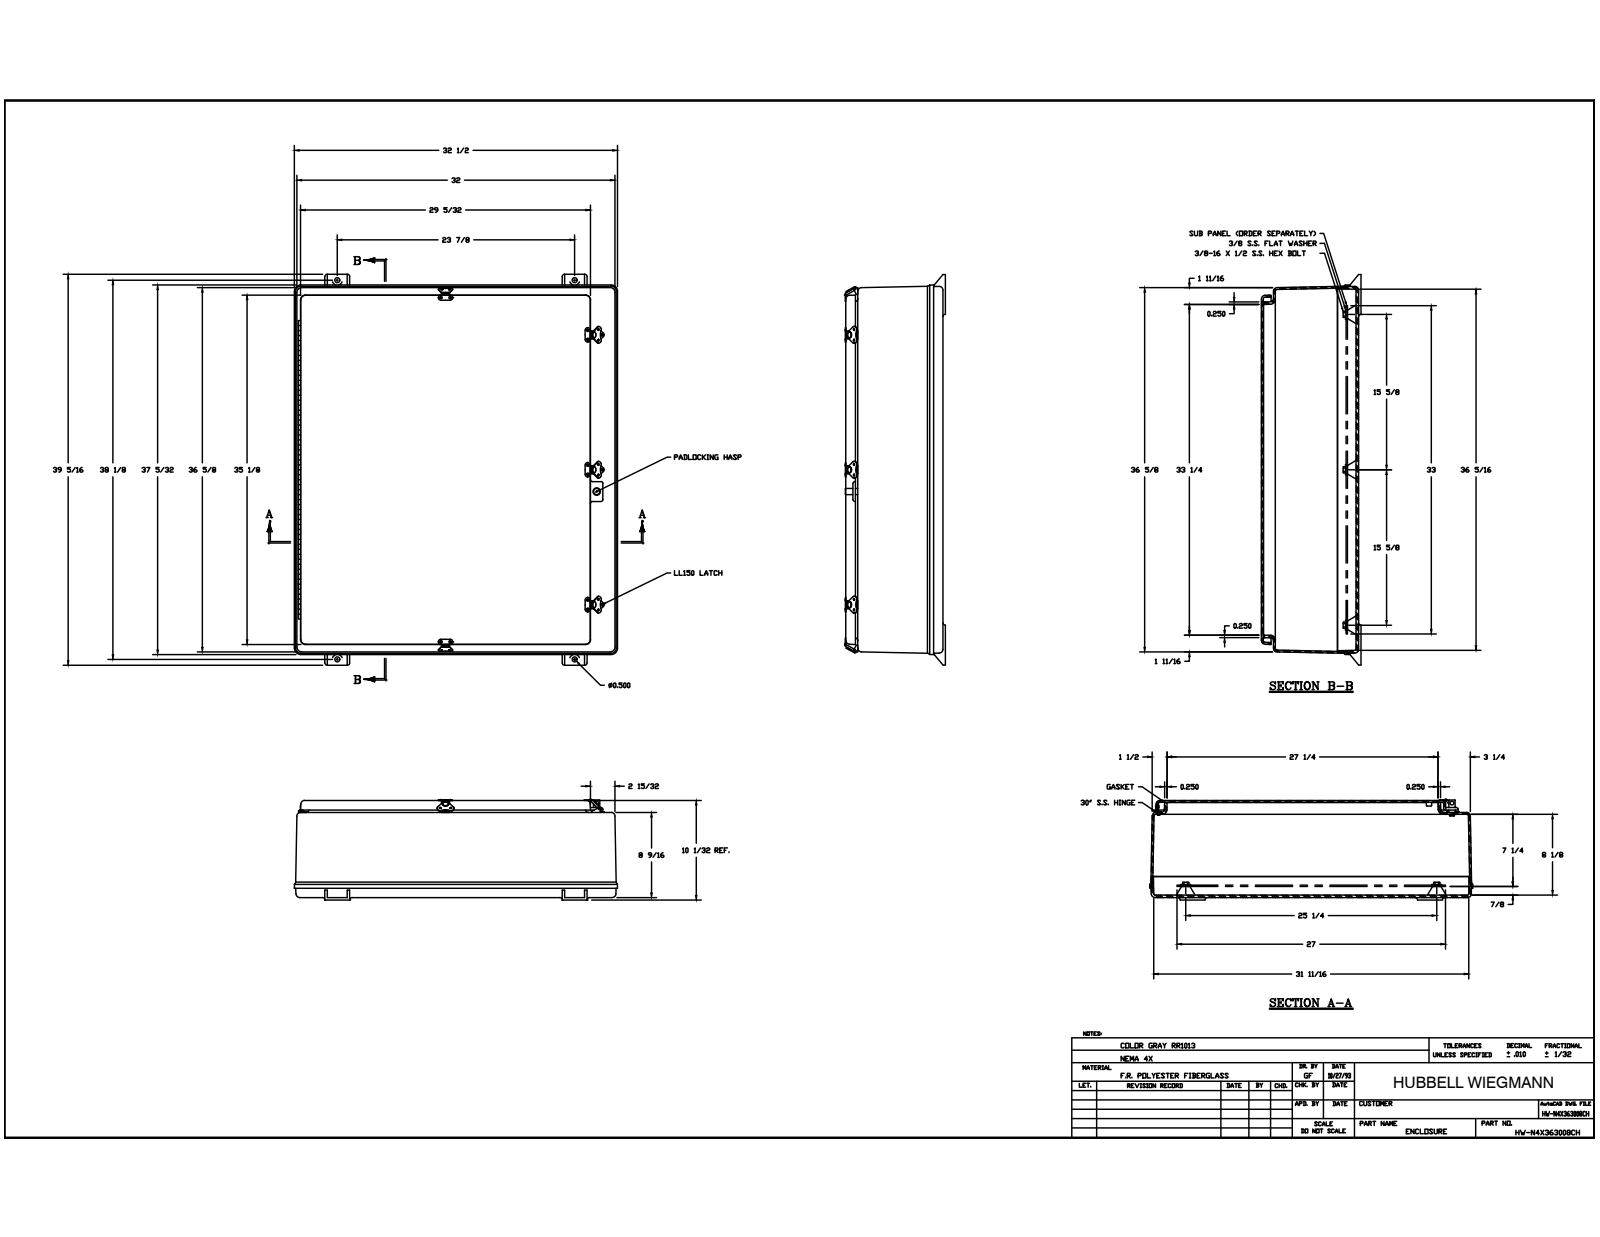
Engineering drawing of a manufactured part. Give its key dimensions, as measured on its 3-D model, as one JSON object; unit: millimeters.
{"part_name": "WPN36308SHWT; WPN3630B; WPN36308HWTPCVR; N36308G (+8 more)", "step_written_by": "Autodesk Inventor 2014 (AUTOMOTIVE_DESIGN)", "units": "millimeters", "bodies": {"solids": 63, "faces": 1832, "planar": 712, "cylindrical": 728, "other": 392}, "overall_size": [998.54, 825.5, 263.29], "volume_mm3": 13490000, "surface_area_mm2": 5332000, "round_holes": [[3.3, 36], [1.59, 20], [3.5, 10], [4.76, 10], [1.65, 8], [14.3, 4], [3.43, 3], [3.97, 3], [11, 2], [12.95, 2], [12.96, 2], [3.17, 1]], "round_bosses_or_shafts": [[3.56, 20], [7.54, 8], [12.7, 5], [5.08, 3], [6.35, 1], [5.11, 1]], "partial_cylinders_radius": [[0.25, 127], [4.76, 25], [6.35, 24], [7.94, 23], [0.76, 20], [9.53, 17], [12.7, 12], [1.59, 10]], "face_to_face_distances": [6.35, 4.78, 248.45, 242.1, 243.67, 237.32, 4.76, 4.77, 217.49, 212.73], "hole_center_spacings": [344.49, 241.3, 495.3, 25.4, 88.25, 345.02, 396.88, 483.71]}
